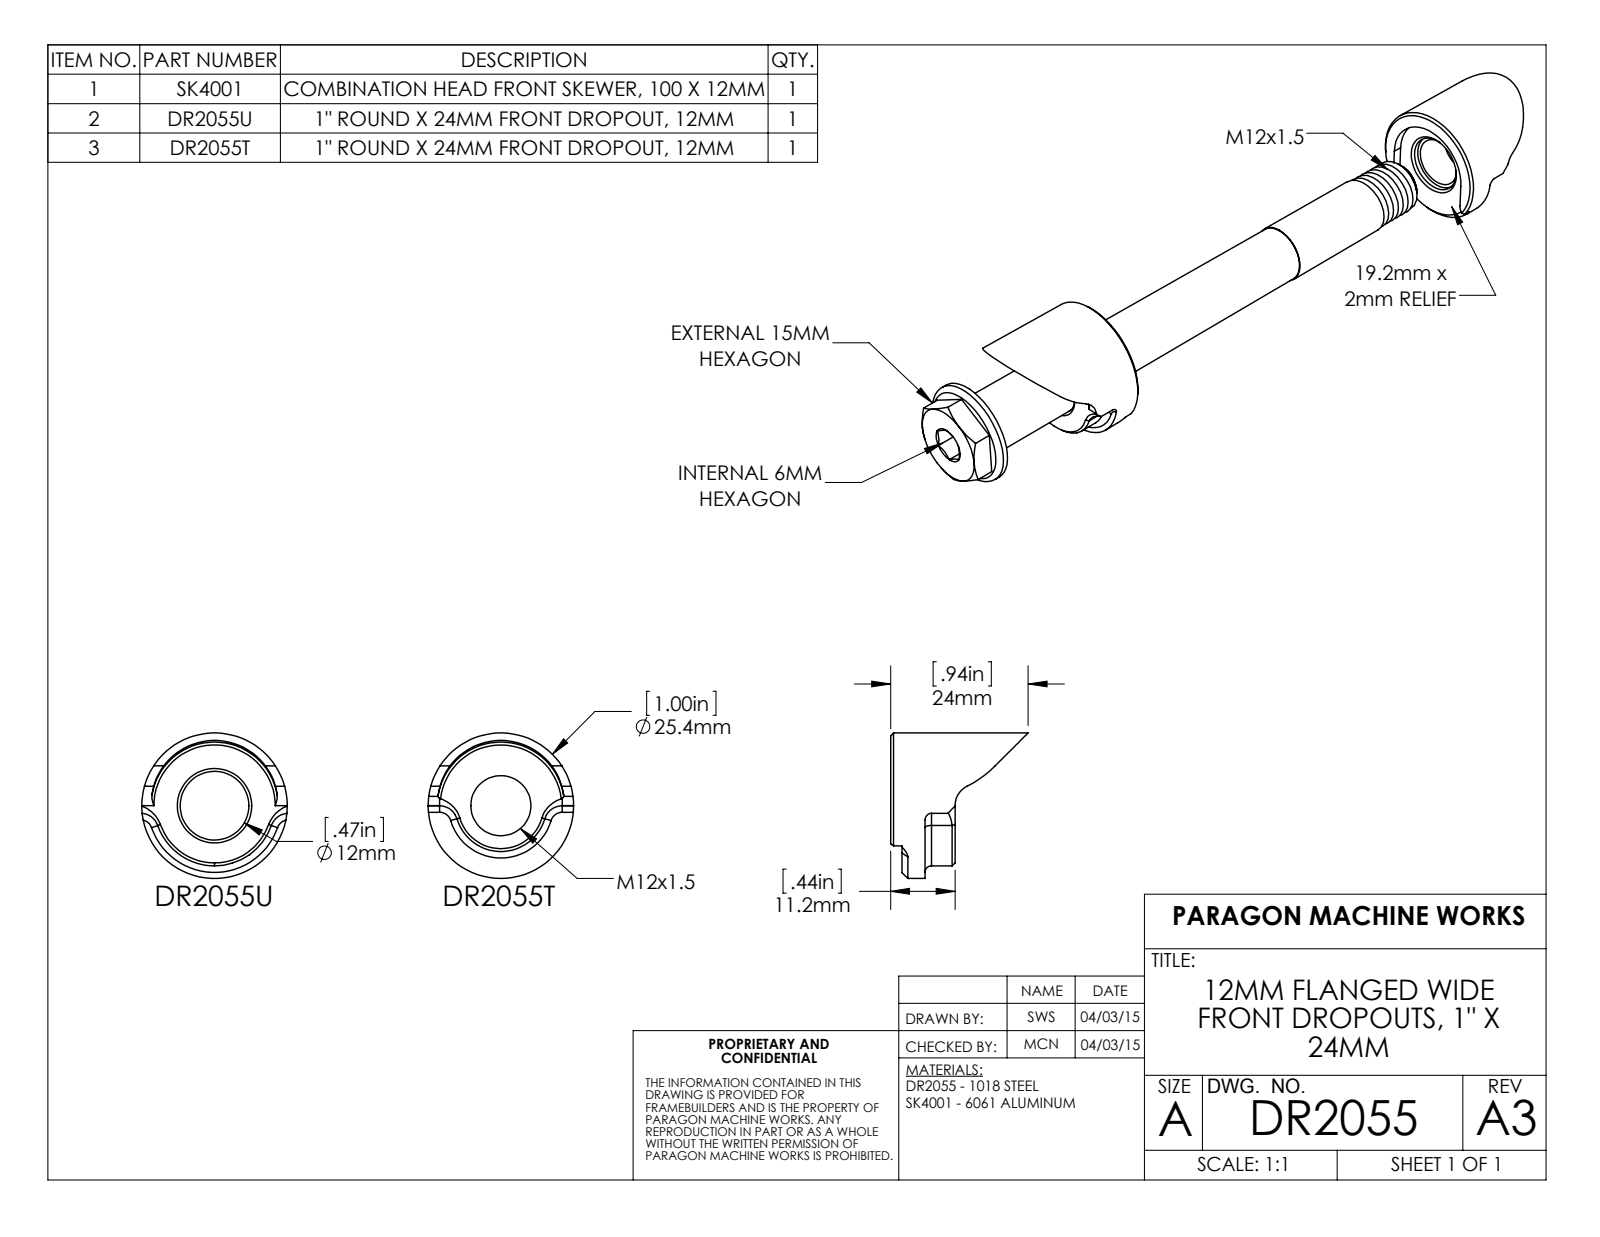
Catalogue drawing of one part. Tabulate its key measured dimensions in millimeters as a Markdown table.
| quantity | value |
| --- | --- |
| part name | DR2055; DR2055T; DR2055U; SK4001 |
| STEP written by | SolidWorks 2015 (AUTOMOTIVE_DESIGN) |
| units | millimeters |
| bodies | 3 solids, 131 faces (38 planar, 38 cylindrical, 55 other) |
| overall size | 144 × 25.4 × 25.4 |
| volume | 21 411 mm³ |
| surface area | 10 811 mm² |
| round holes (diameter × count) | 12 × 1 |
| round bosses / shafts (diameter × count) | 25.4 × 1, 20 × 1, 11.96 × 1, 11.68 × 1 |
| partial cylindrical surfaces (radius × count) | 3.17 × 4, 2.5 × 2, 3.81 × 2, 19.05 × 2, 1.14 × 1, 8 × 1, 9.6 × 1, 10.5 × 1 |
| main face-to-face distances | 109.25, 9.25, 6, 11.25, 2, 113.25, 107.25, 98, 100, 4 |
